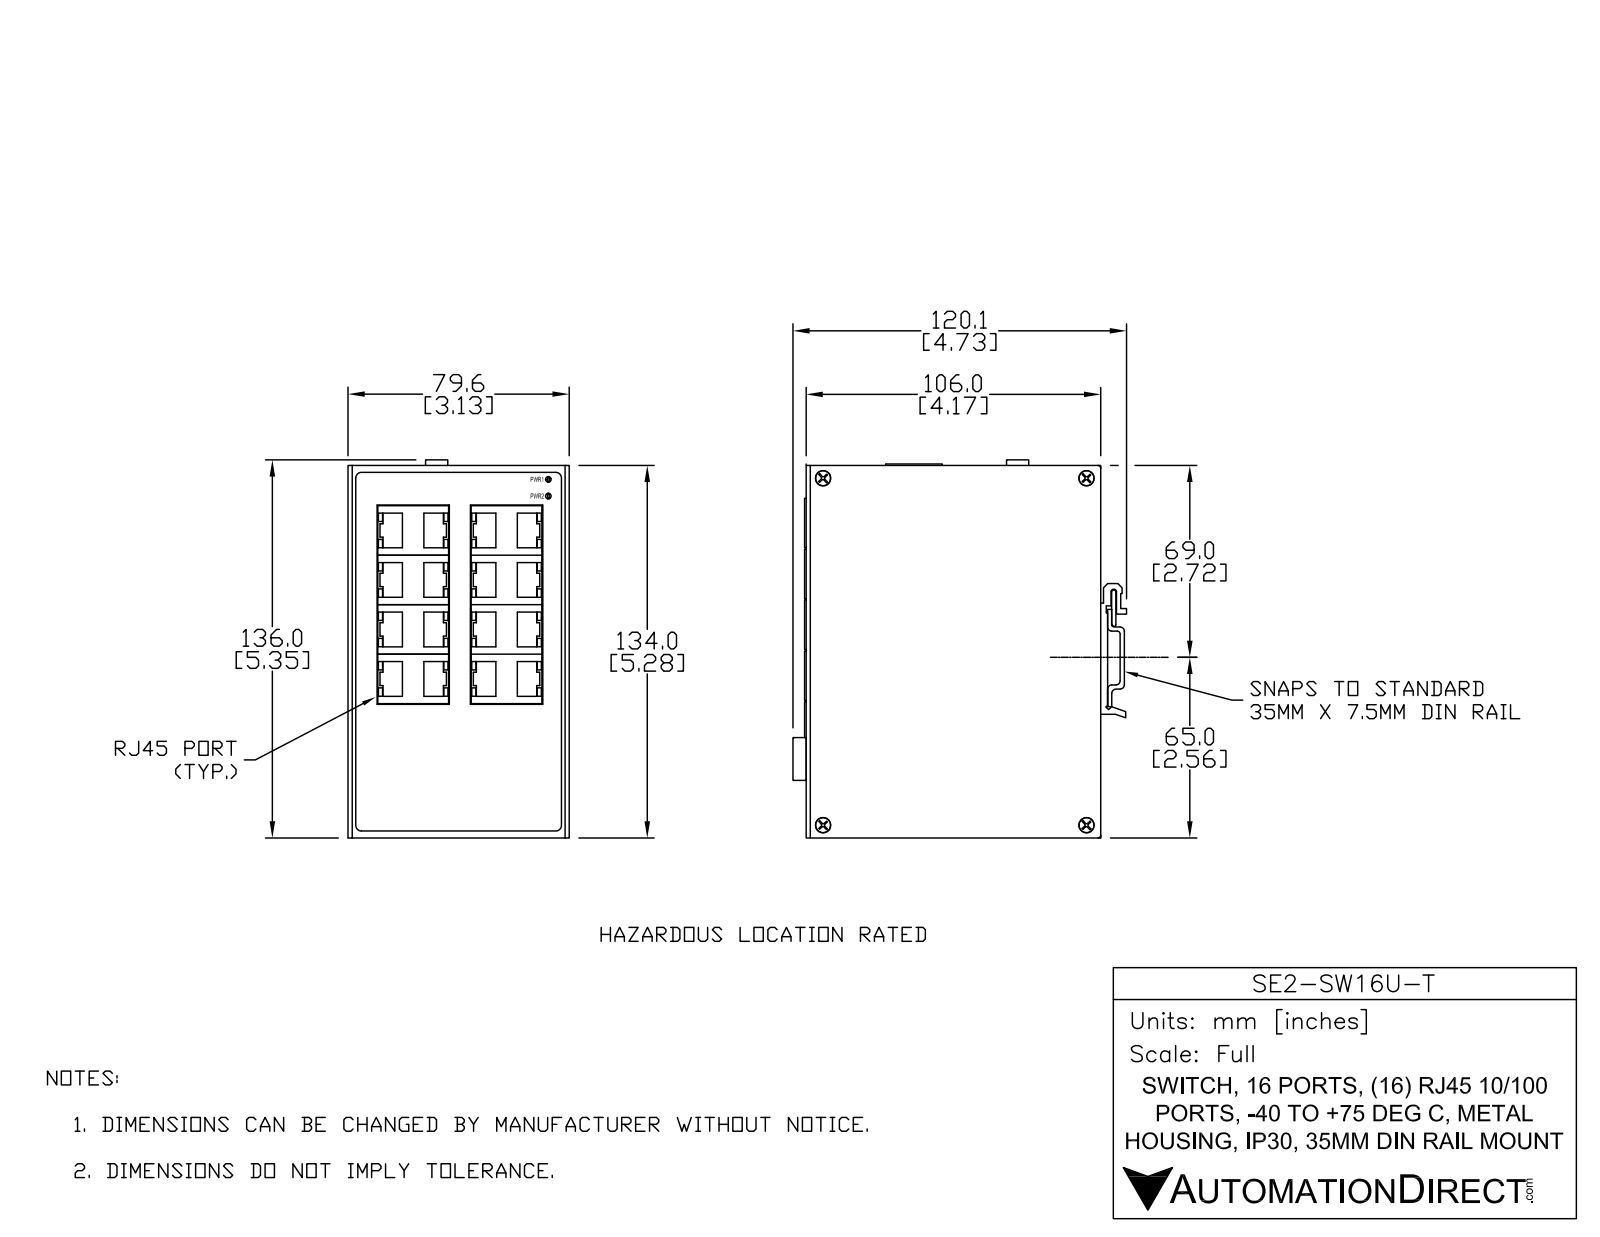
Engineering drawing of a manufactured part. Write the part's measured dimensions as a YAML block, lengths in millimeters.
part_name: "SE2-SW16U-T"
step_written_by: "SolidWorks 2017 (AUTOMOTIVE_DESIGN)"
units: millimeters
bodies: {solids: 44, faces: 2655, planar: 1928, cylindrical: 594, other: 133}
overall_size: [146.3, 116.1, 79.7]
volume: 172600
surface_area: 208400
round_holes:
  - {diameter: 2.5, count: 10}
  - {diameter: 2.8, count: 6}
  - {diameter: 1.3, count: 4}
  - {diameter: 3.8, count: 4}
  - {diameter: 3, count: 2}
  - {diameter: 3.5, count: 2}
  - {diameter: 2, count: 1}
  - {diameter: 5, count: 1}
round_bosses_or_shafts:
  - {diameter: 6.3, count: 10}
  - {diameter: 3.5, count: 10}
  - {diameter: 4.5, count: 8}
  - {diameter: 2.4, count: 8}
  - {diameter: 3.6, count: 4}
  - {diameter: 3, count: 4}
  - {diameter: 1.3, count: 4}
  - {diameter: 8, count: 1}
partial_cylinders:
  - {radius: 0.6, count: 252}
  - {radius: 0.3, count: 4}
  - {radius: 1.1, count: 4}
  - {radius: 1.1, count: 4}
  - {radius: 2, count: 4}
  - {radius: 2.8, count: 4}
  - {radius: 2.9, count: 4}
  - {radius: 2.9, count: 4}
face_to_face_distances: [1, 1, 1, 1.9, 133, 77.5, 78.5, 79.5, 78.5, 0.9]
hole_center_spacings: [5.1, 20, 5.2, 10.2, 10.2, 16, 34.9, 40]
